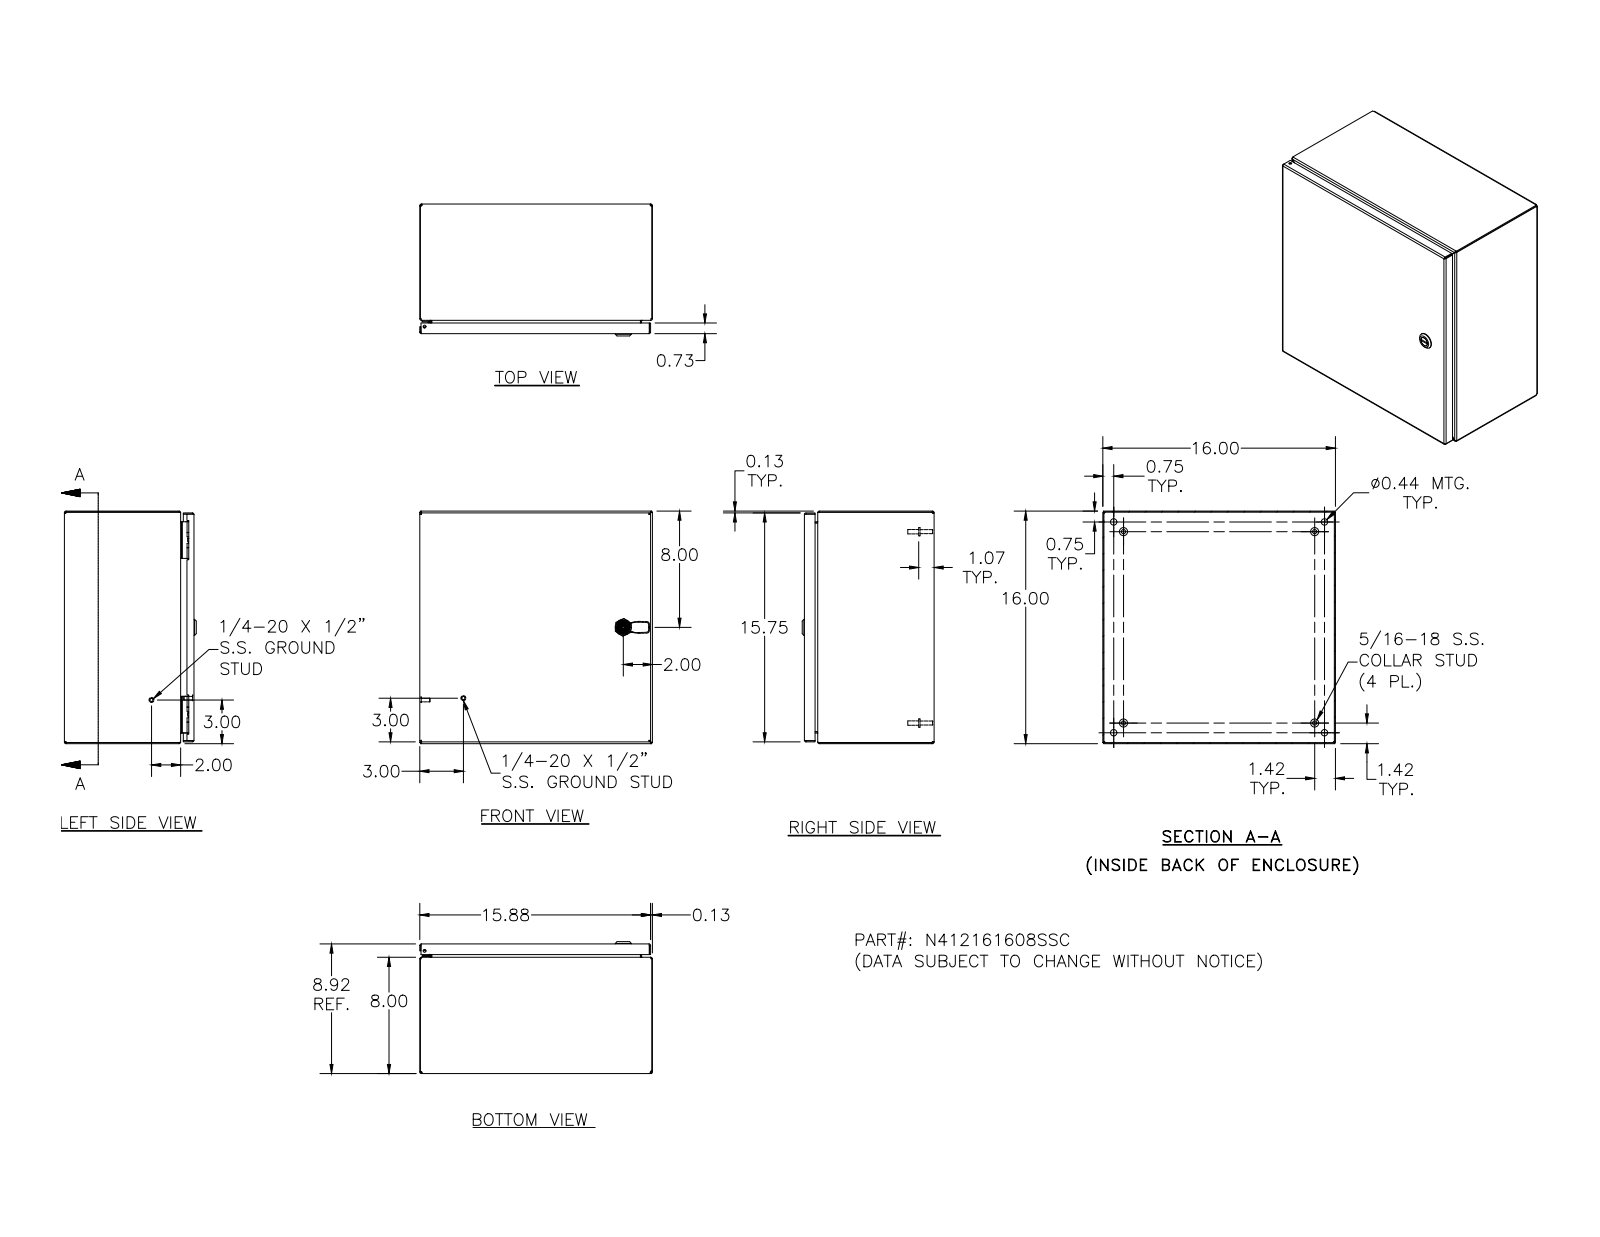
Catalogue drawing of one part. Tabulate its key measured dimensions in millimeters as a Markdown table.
| quantity | value |
| --- | --- |
| part name | N412161608SSC; NA12161608SSCBKP; 388151; N4121616SSCLID (+8 more) |
| STEP written by | Autodesk Inventor 2011 (AUTOMOTIVE_DESIGN) |
| units | millimeters |
| bodies | 34 solids, 1384 faces (531 planar, 509 cylindrical, 344 other) |
| overall size | 406.4 × 406.4 × 230.5 |
| volume | 1 405 000 mm³ |
| surface area | 1 506 000 mm² |
| round holes (diameter × count) | 4.8 × 5, 2.4 × 4, 3.9 × 4, 4.2 × 4, 4.4 × 4, 11.1 × 4, 4 × 2, 4.7 × 1, 5 × 1, 8 × 1, 10 × 1, 10.2 × 1 |
| round bosses / shafts (diameter × count) | 6.4 × 10, 14.3 × 4, 9.1 × 4, 8.1 × 4, 7.6 × 4, 7 × 4, 6.5 × 4, 4.2 × 4 |
| partial cylindrical surfaces (radius × count) | 0.8 × 30, 1.3 × 26, 2.7 × 20, 0.4 × 18, 3.2 × 14, 0.5 × 9, 0.8 × 8, 1.8 × 8 |
| main face-to-face distances | 1.9, 404.5, 224.6, 406.4, 402.6, 222.7, 226.5, 201.3, 23.3, 385.7 |
| hole center spacings | 304.8, 0.4, 16.8, 368.3, 0.5, 12.7, 16.5, 16.6 |
